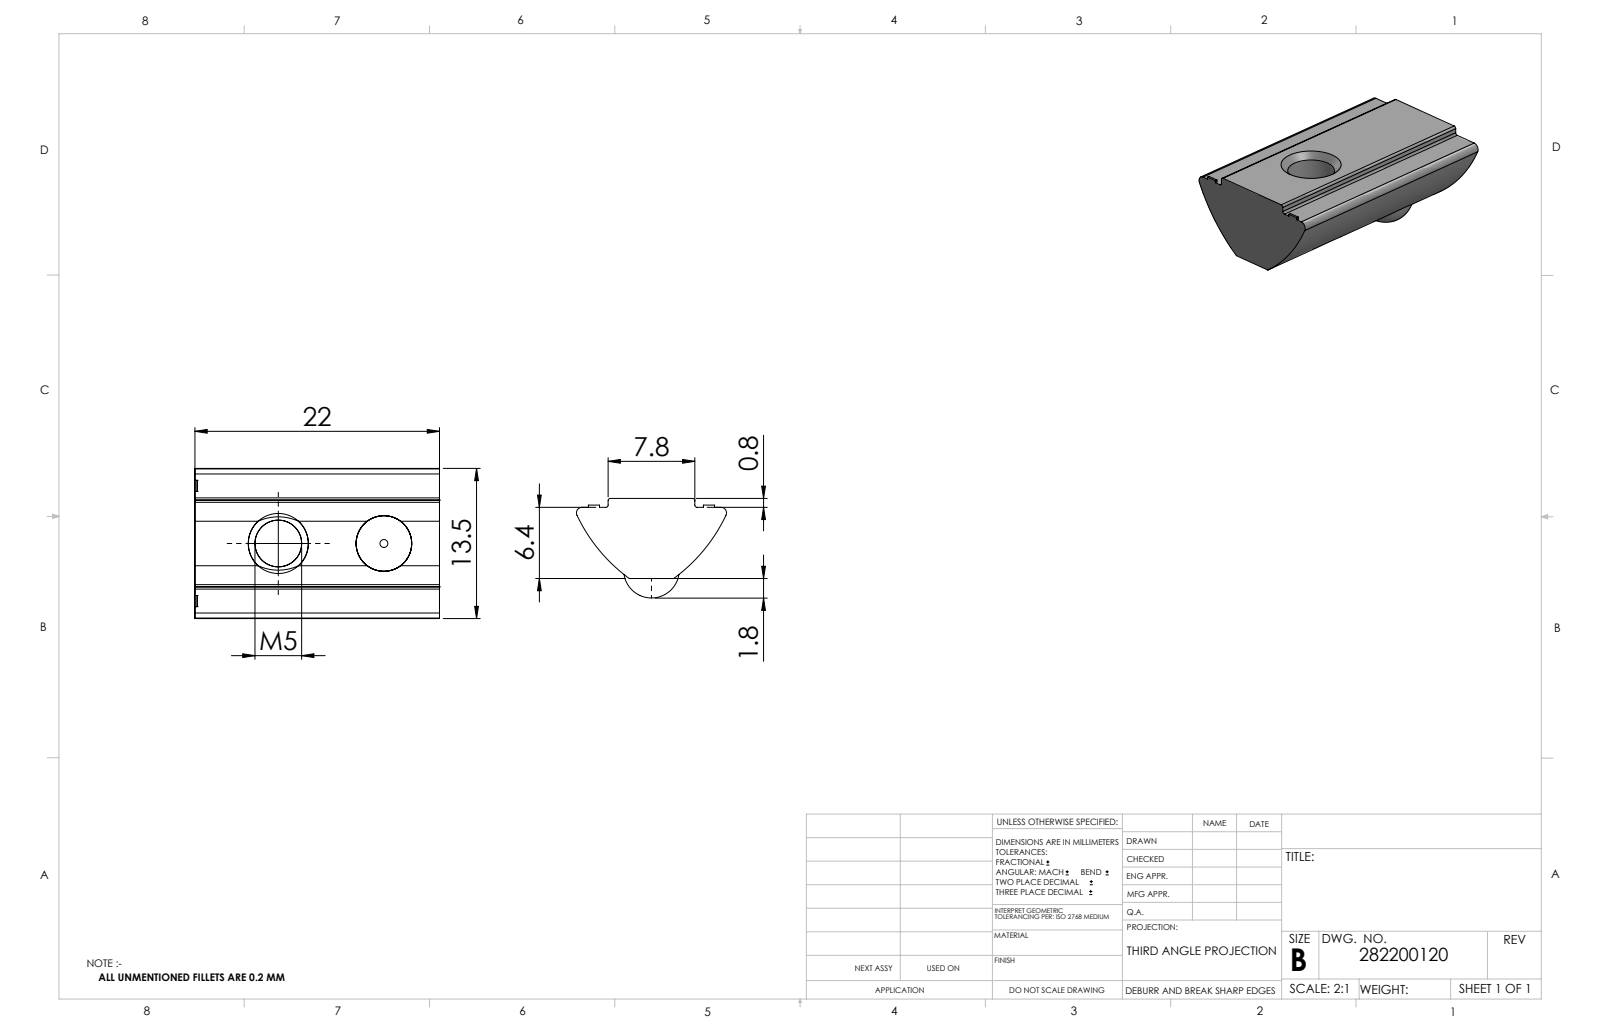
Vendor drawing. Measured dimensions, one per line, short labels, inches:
name: 282200120_c_1
written by: SolidWorks 2014 (CONFIG_CONTROL_DESIGN)
unit: in
bodies: 2 solids, 40 faces (19 planar, 13 cylindrical, 8 other)
size: 0.866 × 0.531 × 0.352
volume: 0.084 in³; area: 1.758 in²
holes: 1× ⌀0.165, 1× ⌀0.197
rounds: 4× R0.008, 2× R0.02, 2× R0.591
face distances: 0.031, 0.866, 0.252, 0.283, 0.307, 0.024, 0.858, 0.26, 0.276, 0.016
hole spacings: 0.374
